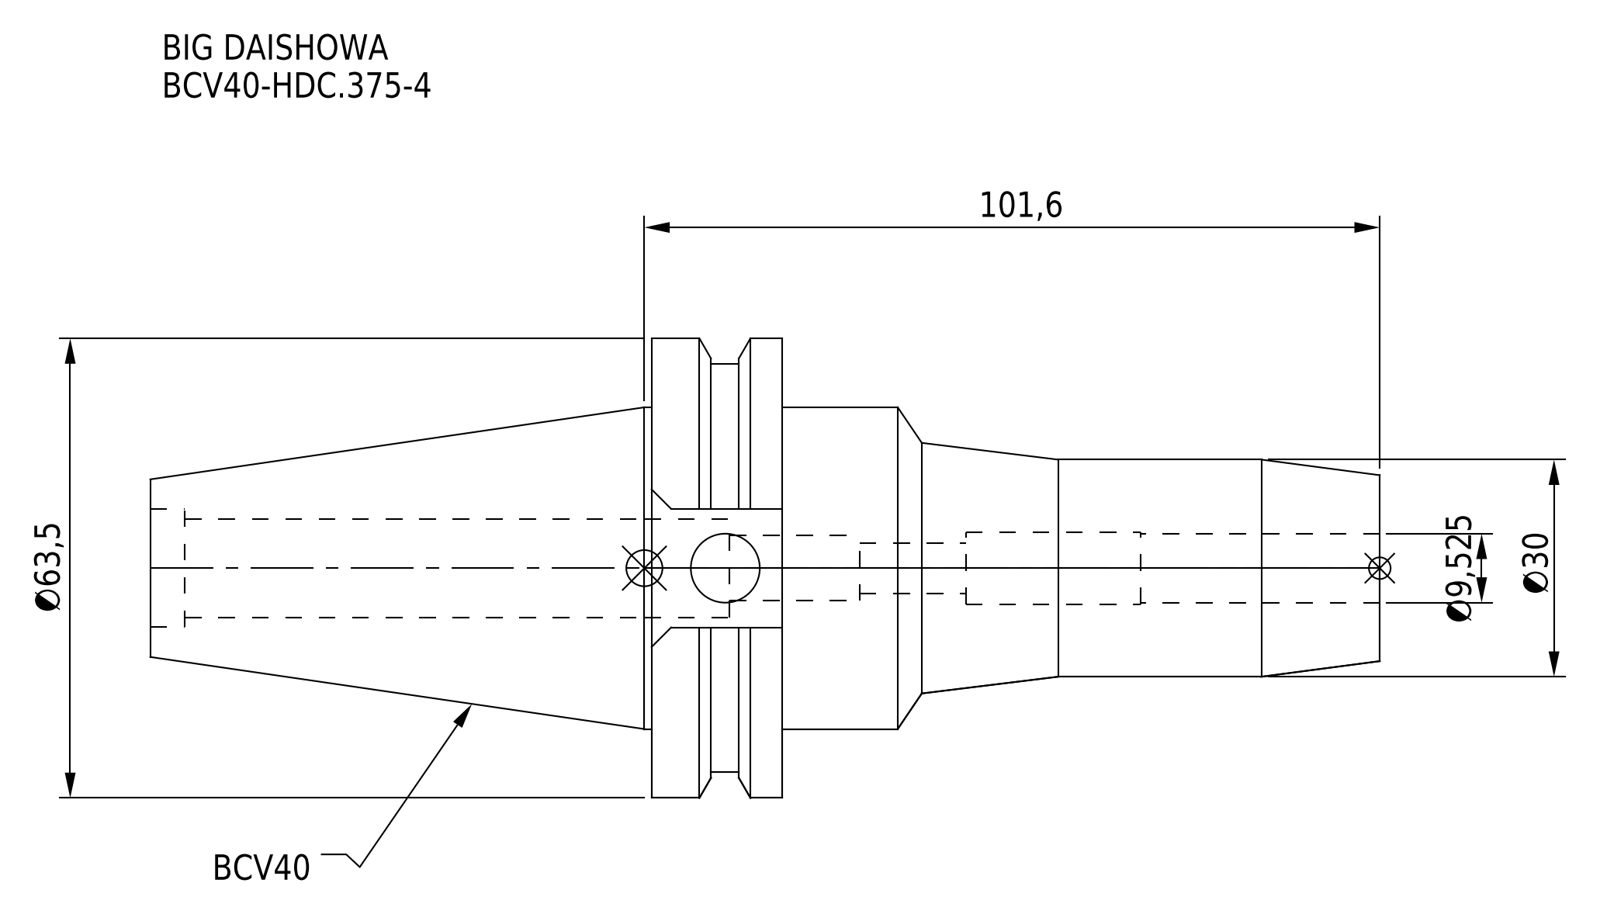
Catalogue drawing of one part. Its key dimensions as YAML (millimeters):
part_name: "BCV40-HDC_375-4"
step_written_by: "CREO PARAMETRIC BY PTC INC, 2016380 (AUTOMOTIVE_DESIGN)"
units: millimeters
bodies: {solids: 1, faces: 64, planar: 24, cylindrical: 28, other: 12}
overall_size: [169.85, 63.5, 61.35]
volume: 173068
surface_area: 30896
round_holes:
  - {diameter: 9.53, count: 2}
  - {diameter: 7, count: 1}
  - {diameter: 9, count: 1}
  - {diameter: 10, count: 1}
  - {diameter: 13.6, count: 1}
  - {diameter: 16.32, count: 1}
round_bosses_or_shafts:
  - {diameter: 63.5, count: 1}
  - {diameter: 56.36, count: 1}
  - {diameter: 44.45, count: 1}
  - {diameter: 30, count: 1}
face_to_face_distances: [18.05, 82.55, 100.6, 169.85, 87.3, 69.25, 47.55, 16.38, 88.55, 6]
